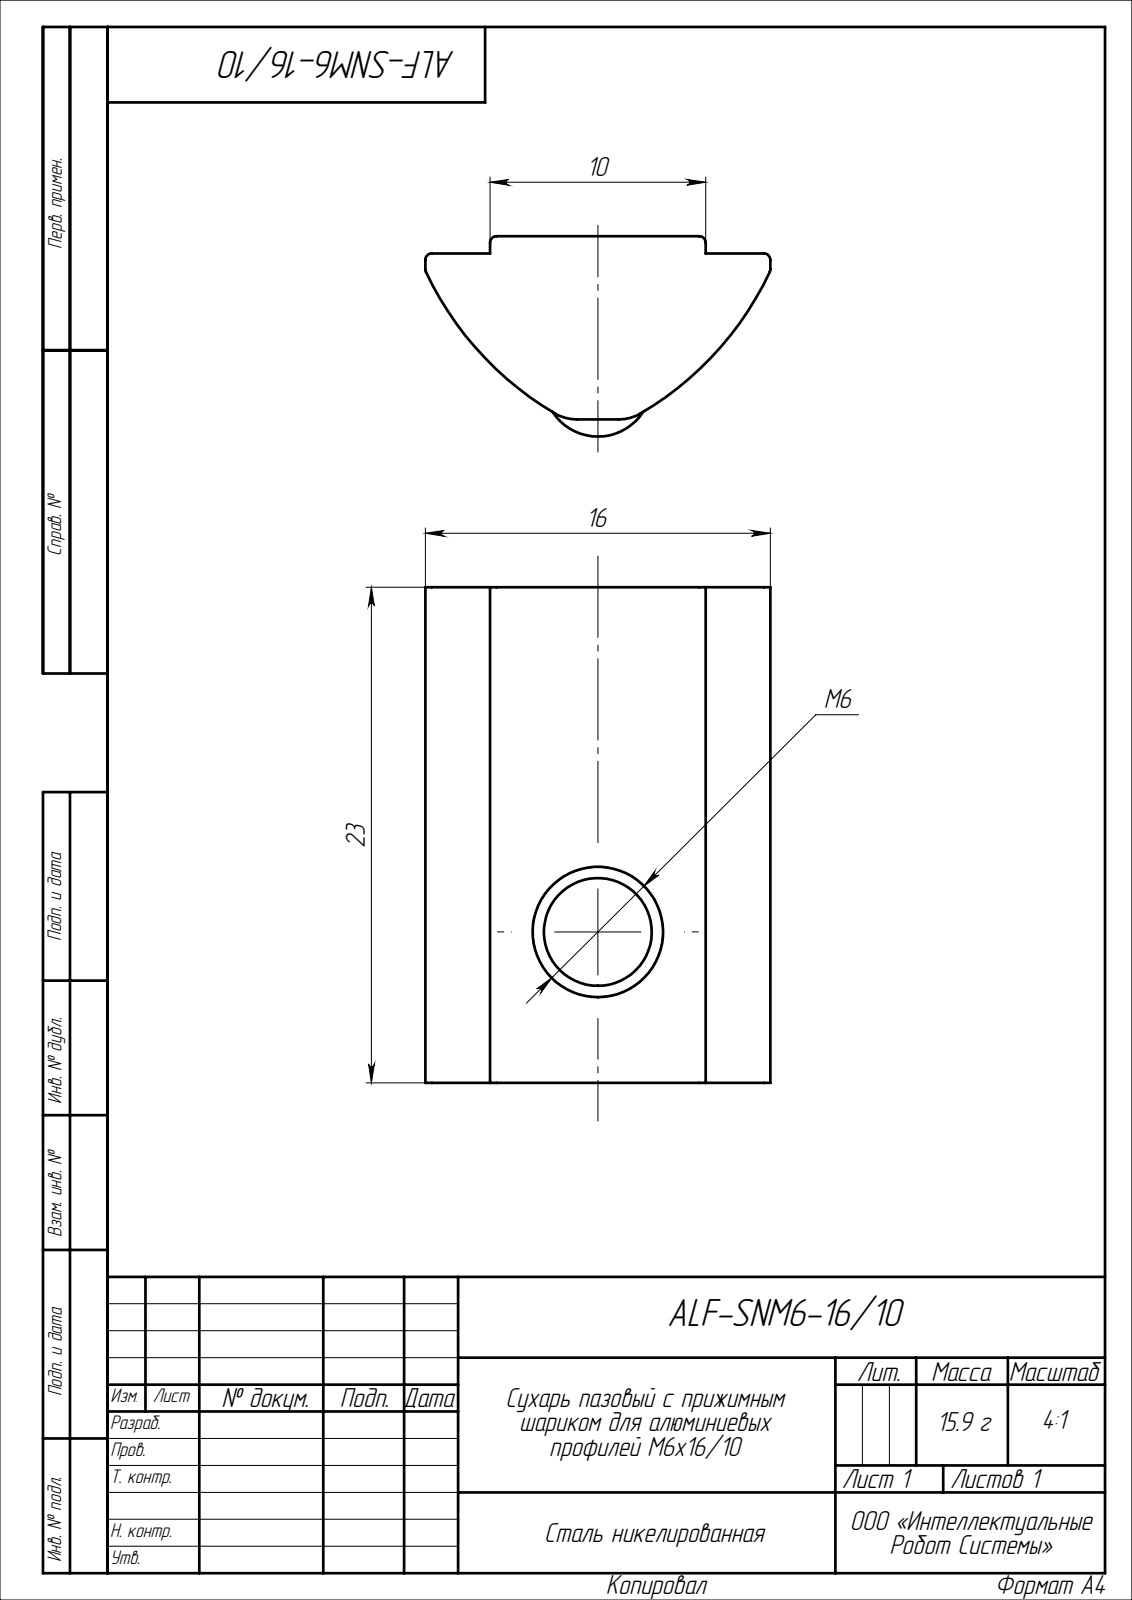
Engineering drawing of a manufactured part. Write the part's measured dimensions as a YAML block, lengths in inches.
part_name: "ALF-SNM6-16_10"
step_written_by: "SolidWorks 2022 (CONFIG_CONTROL_DESIGN)"
units: inches
bodies: {solids: 1, faces: 32, planar: 12, cylindrical: 16, other: 4}
overall_size: [0.906, 0.63, 0.366]
volume: 0.125
surface_area: 1.893
round_holes:
  - {diameter: 0.197, count: 1}
partial_cylinders:
  - {radius: 0.012, count: 6}
  - {radius: 0.079, count: 2}
  - {radius: 0.591, count: 2}
face_to_face_distances: [0.031, 0.906, 0.303, 0.335, 0.118, 0.512, 0.394, 0.63]
